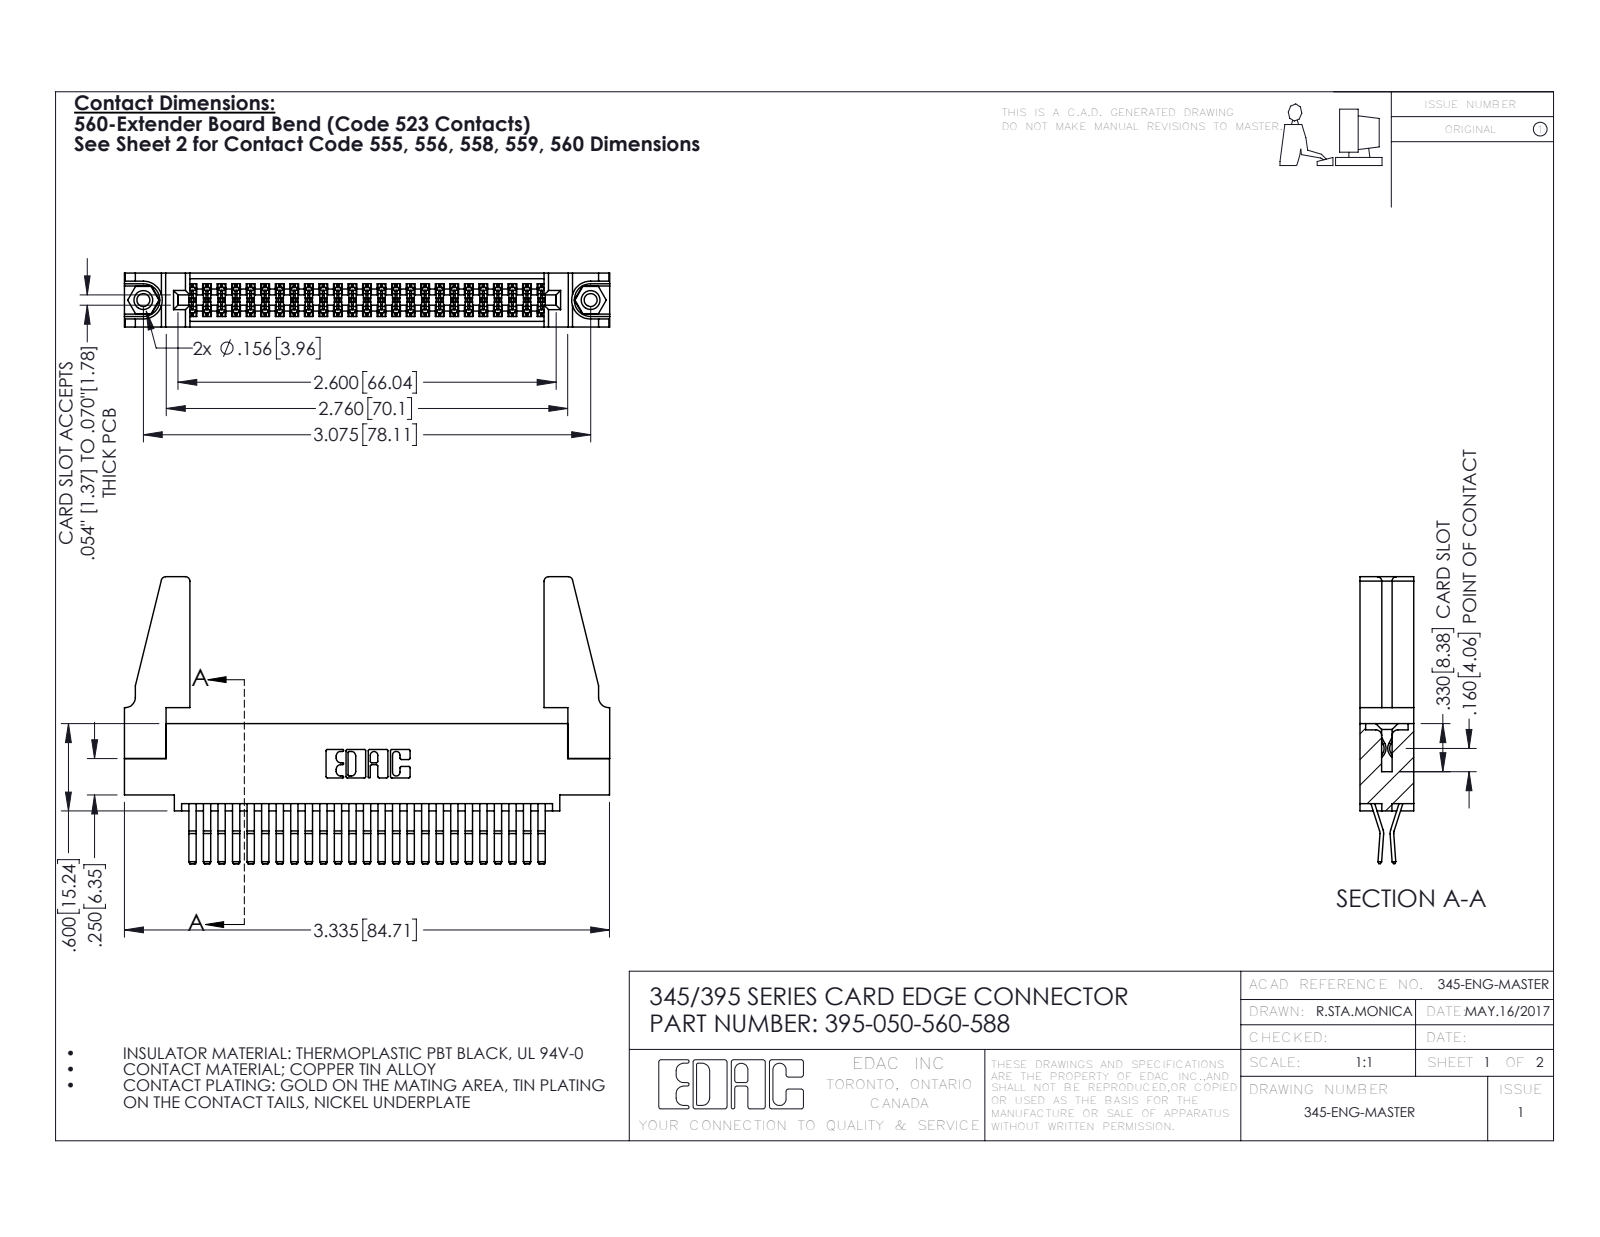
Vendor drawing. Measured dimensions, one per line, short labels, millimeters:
name: 345-292-001_560 Tail; 345-220-078_345-220-088; 345-250-001_345-250-001-102; 395-050-560-588 (+1 more)
written by: SolidWorks 2016 (CONFIG_CONTROL_DESIGN)
unit: mm
bodies: 55 solids, 2854 faces (1806 planar, 1032 cylindrical, 16 other)
size: 84.7 × 50.1 × 9.4
volume: 11 600 mm³; area: 16 040 mm²
holes: 2× ⌀2.3, 2× ⌀3.2, 2× ⌀4, 1× ⌀1.6
bosses: 2× ⌀3.9
rounds: 76× R0.2, 22× R0.3, 8× R0.8, 6× R0.2, 6× R0.8, 3× R0.7, 2× R0.3, 2× R0.4
face distances: 1.8, 9.4, 7.6, 0.6, 5.1, 2.5, 6.9, 5.7, 4.4, 3.8
hole spacings: 6.9, 72.1, 78.1
